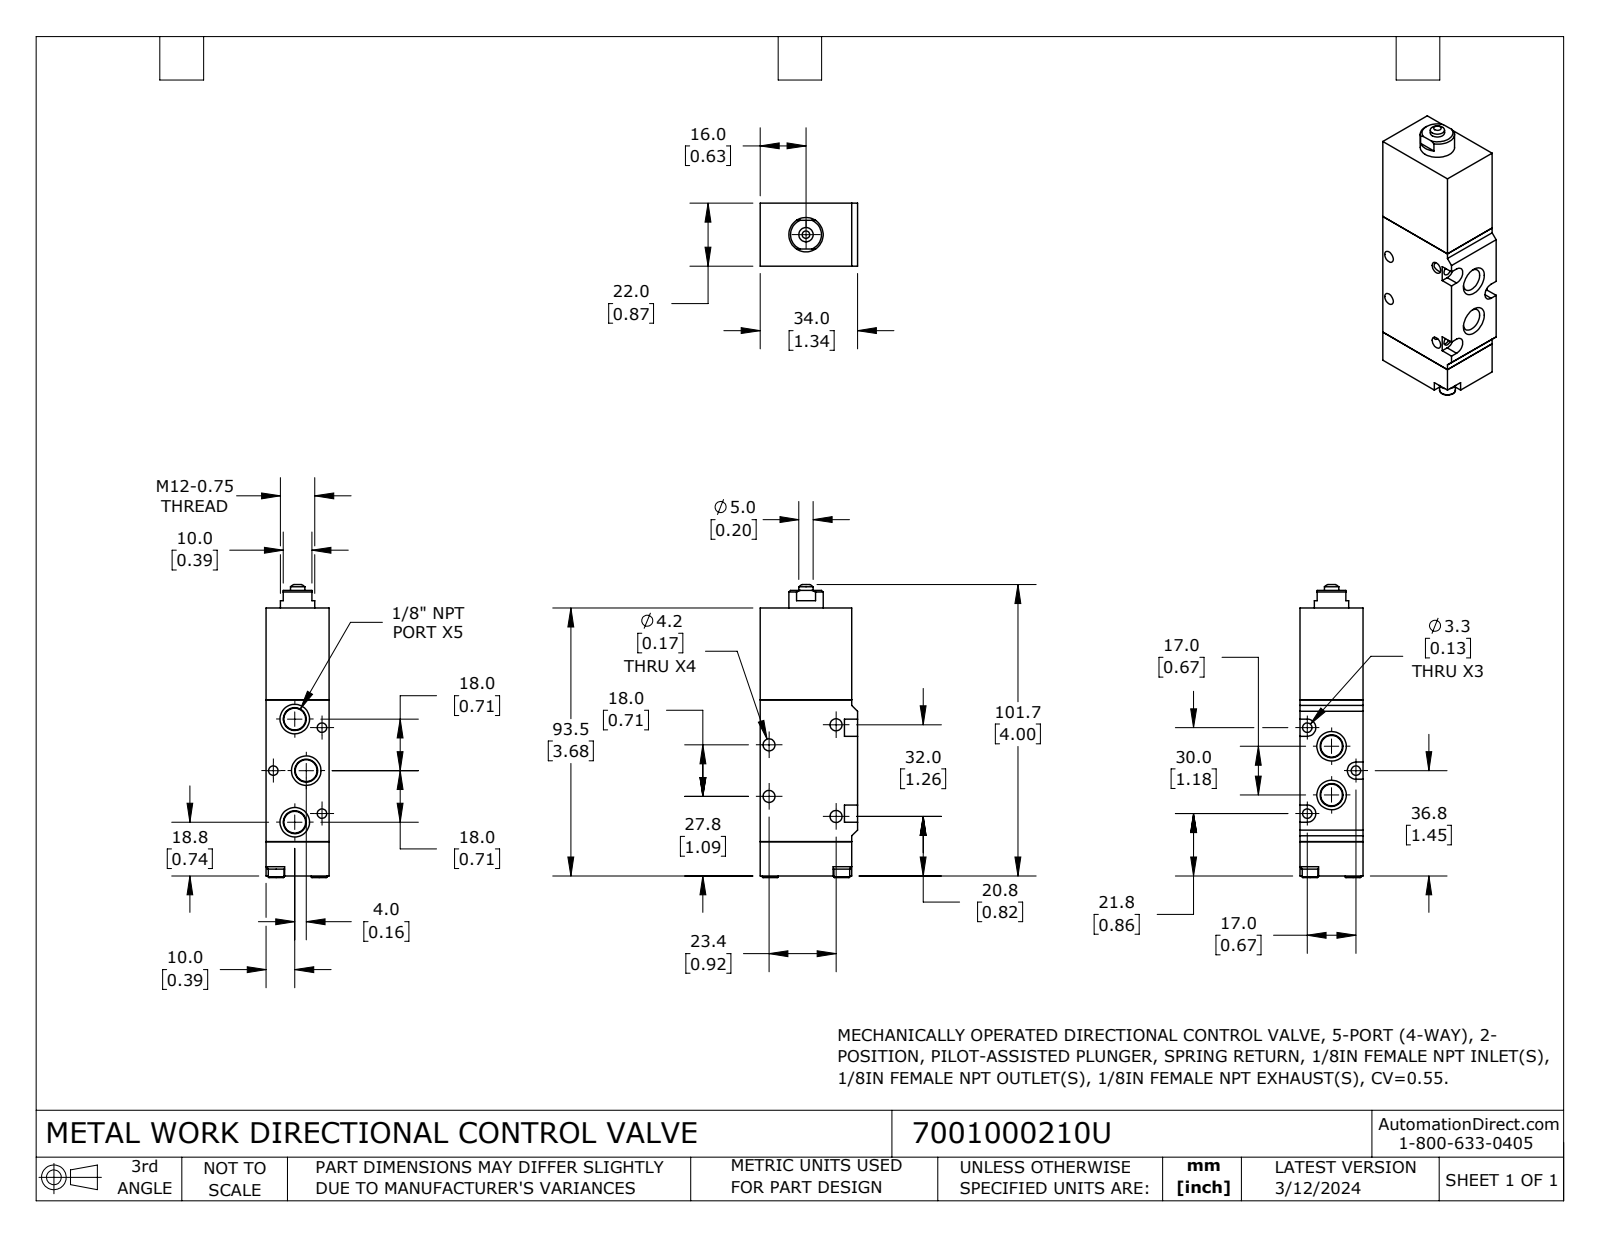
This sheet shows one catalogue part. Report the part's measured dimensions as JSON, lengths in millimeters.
{"part_name": "7001000210U", "step_written_by": "SolidWorks 2023 (CONFIG_CONTROL_DESIGN)", "units": "millimeters", "bodies": {"solids": 7, "faces": 177, "planar": 82, "cylindrical": 43, "other": 52}, "overall_size": [102.3, 34, 22], "volume_mm3": 64220, "surface_area_mm2": 18120, "round_holes": [[4.2, 4], [3.3, 3], [3, 2]], "round_bosses_or_shafts": [[6, 2], [5.5, 2], [12, 1], [5, 1]], "partial_cylinders_radius": [[3, 3]], "face_to_face_distances": [22, 32, 49.5, 2, 34, 12, 61.5, 93.5, 81.5, 7.7], "hole_center_spacings": [22.7, 24.4, 34.2, 18, 29.2, 30, 32]}
